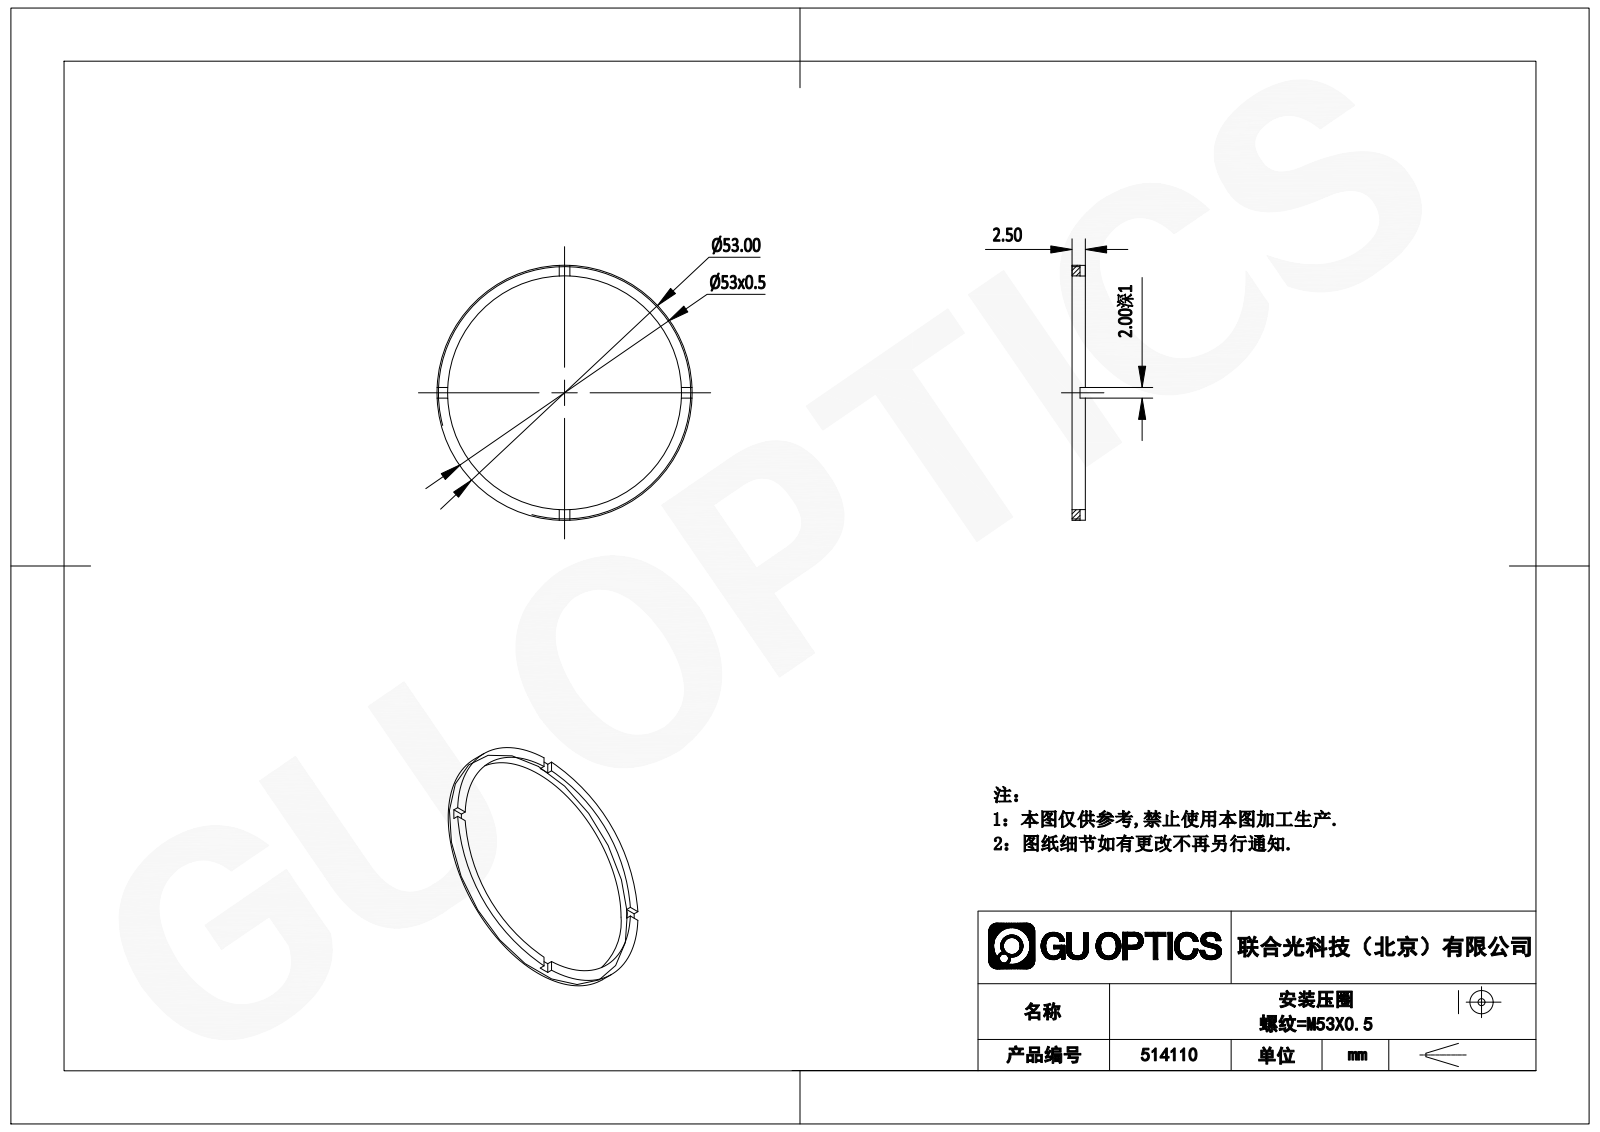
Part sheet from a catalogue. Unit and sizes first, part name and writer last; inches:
Units: inches
Overall size (bounding box): 2.087 × 2.087 × 0.098
Round holes (diameter × count): ⌀1.89 ×1
Round bosses / shafts (diameter × count): ⌀2.087 ×1
Main face-to-face distances: 0.098, 0.059, 0.039, 0.079
Volume: 0.059 in³ · Surface area: 2.466 in²
Bodies: 1 solid, 21 faces (17 planar, 4 cylindrical, 0 other)
Part name (STEP PRODUCT): 514110
STEP written by: SolidWorks 2020 (CONFIG_CONTROL_DESIGN)
